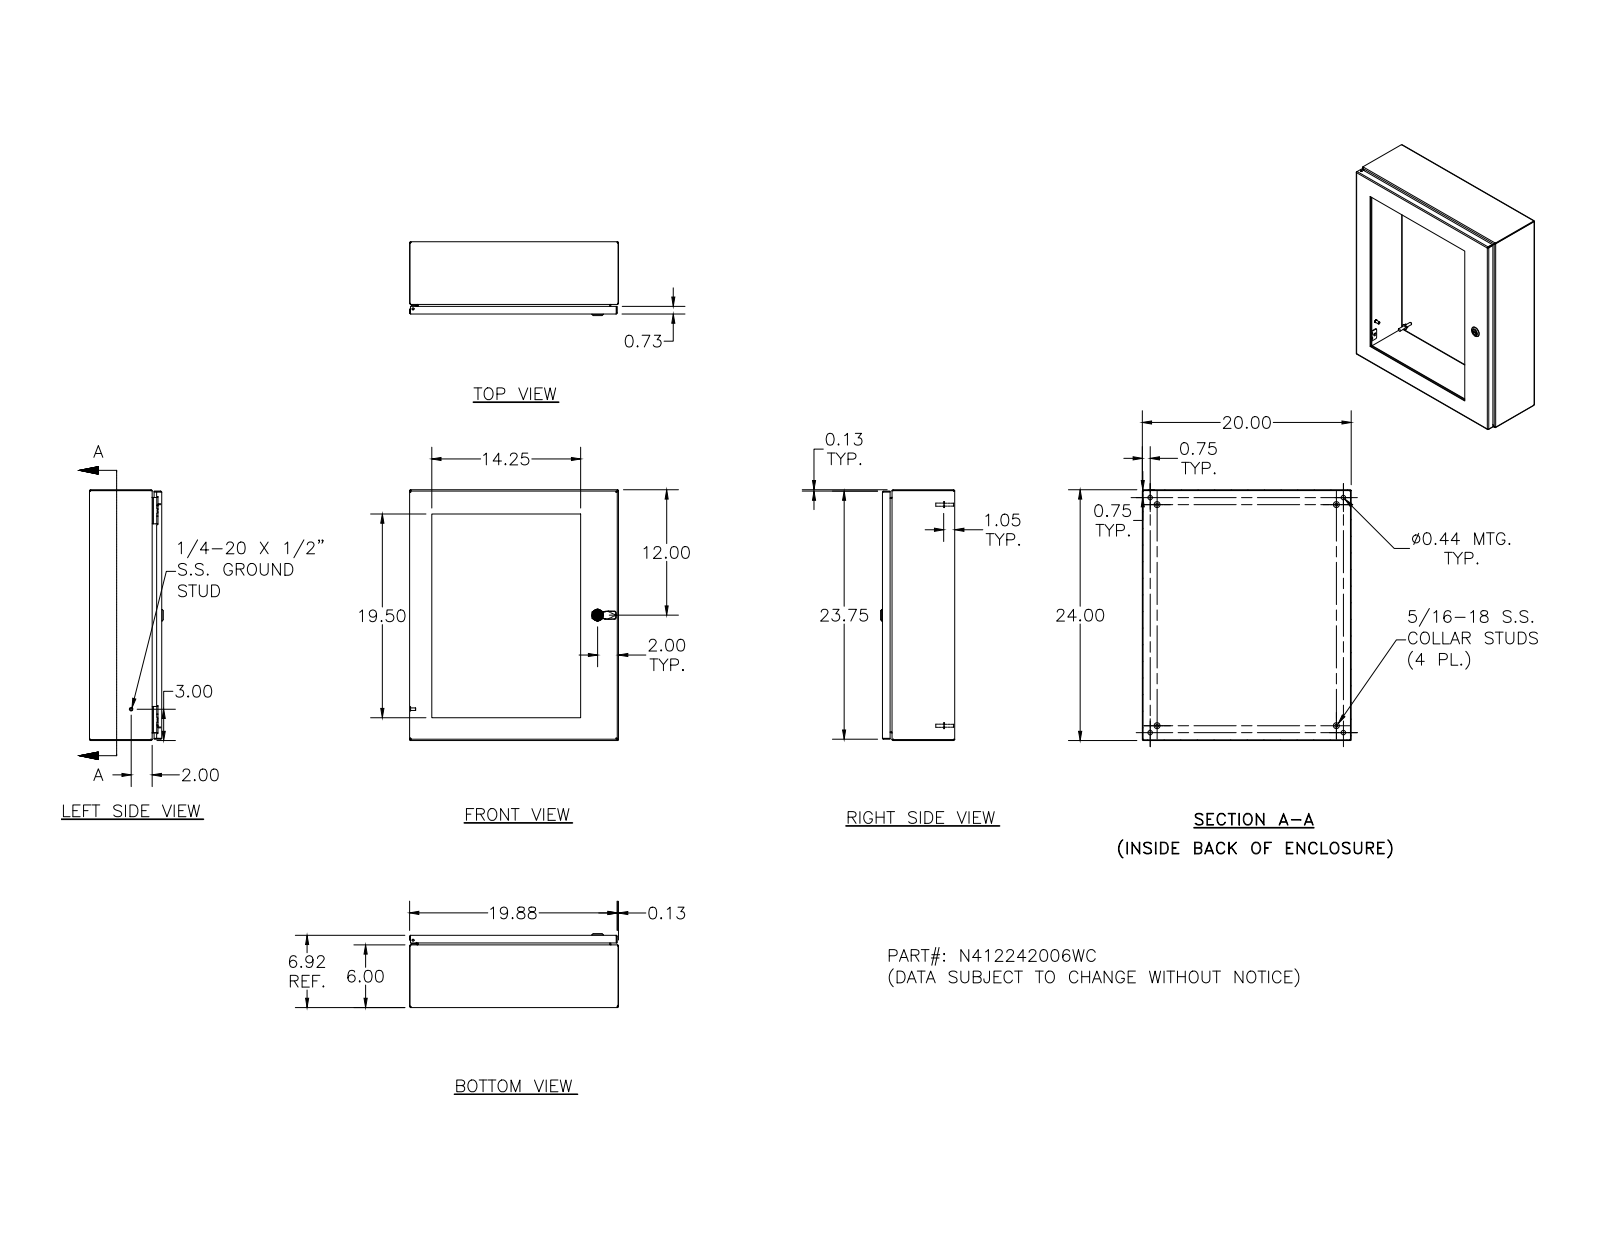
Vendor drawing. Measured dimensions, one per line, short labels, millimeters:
name: N412242006WC
written by: SolidWorks 2018 (AUTOMOTIVE_DESIGN)
unit: mm
bodies: 73 solids, 2083 faces (775 planar, 625 cylindrical, 683 other)
size: 609.6 × 508 × 179.7
volume: 3 063 000 mm³; area: 2 336 000 mm²
holes: 20× ⌀4, 18× ⌀7.1, 5× ⌀4.8, 4× ⌀2.4, 4× ⌀3.9, 4× ⌀4.2, 4× ⌀4.4, 4× ⌀11.1, 1× ⌀4.7, 1× ⌀5, 1× ⌀8, 1× ⌀10
bosses: 18× ⌀8.6, 18× ⌀4.8, 10× ⌀6.4, 4× ⌀14.3, 4× ⌀9.1, 4× ⌀8.1, 4× ⌀7.6, 4× ⌀7
rounds: 34× R0.8, 30× R0.3, 26× R1.3, 24× R2.7, 18× R0.4, 16× R3.2, 13× R0.5, 8× R0.8
face distances: 1.9, 173.8, 171.9, 6.4, 167.5, 165.6, 506.1, 607.7, 175.7, 8.2
hole spacings: 101.6, 203.2, 406.6, 304.8, 443.1, 508, 536.8, 393.7
